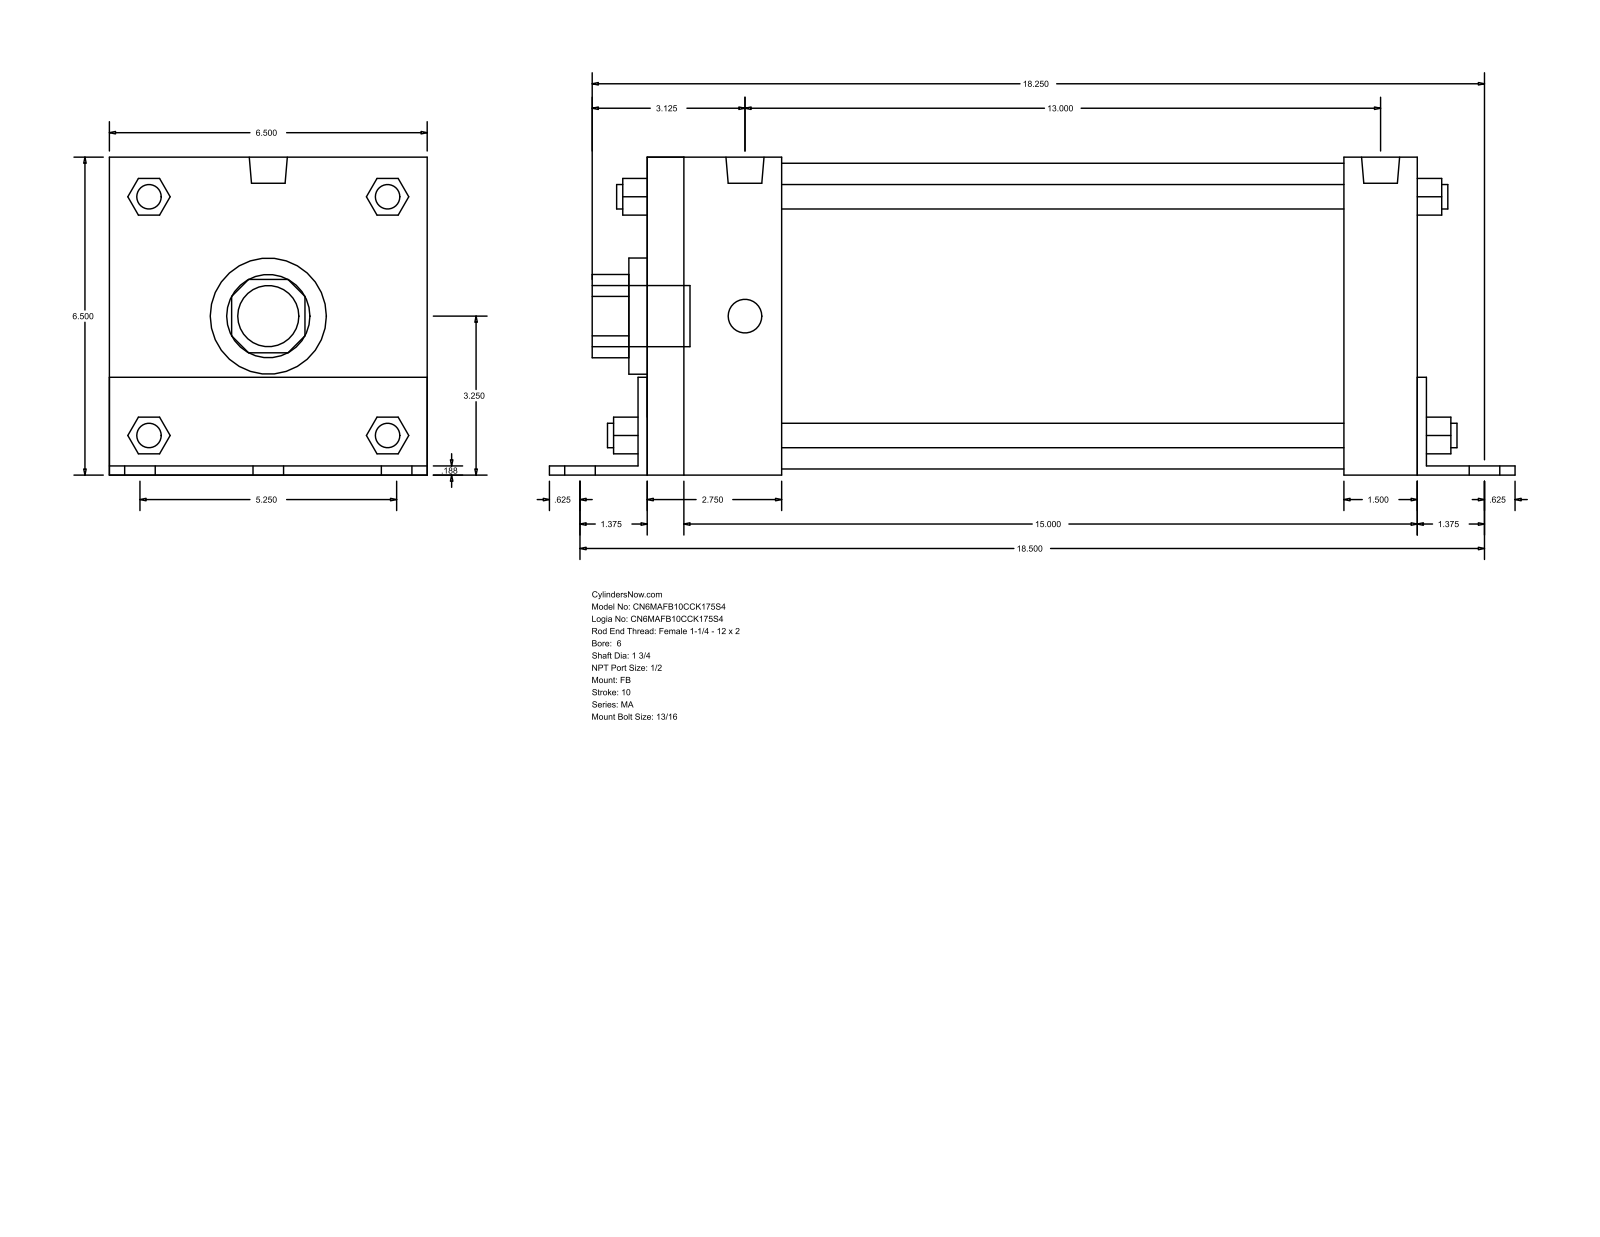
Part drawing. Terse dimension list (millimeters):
name: MA_FB__0600_1.75
written by: GSSL Pune (CONFIG_CONTROL_DESIGN)
unit: mm
bodies: 0 solids, 140 faces (105 planar, 35 cylindrical, 0 other)
size: 501.65 × 165.15 × 165.1
holes: 1× ⌀44.45, 1× ⌀60.33, 1× ⌀158.75
bosses: 6× ⌀20.64, 4× ⌀17.46, 4× ⌀12.7, 2× ⌀19.77, 1× ⌀31.75
rounds: 1× R21.63, 1× R32.05
face distances: 165.1, 4.76, 400.05, 165.15, 4.71, 160.39, 38.1, 4.77, 404.82, 404.81
